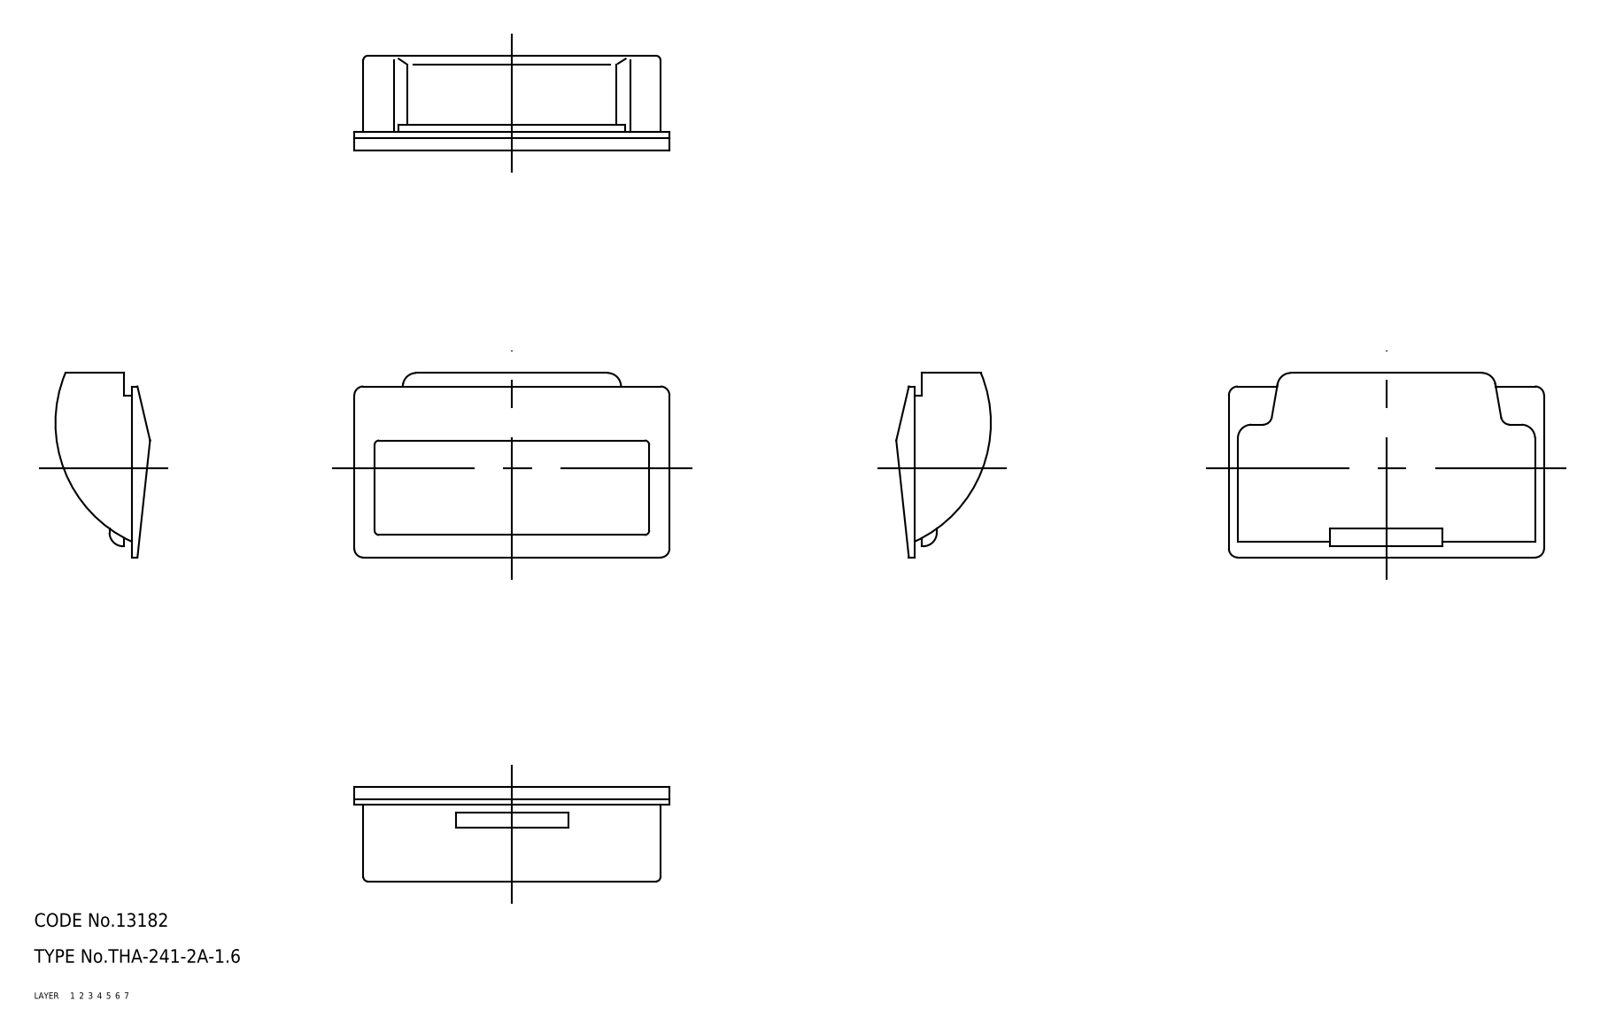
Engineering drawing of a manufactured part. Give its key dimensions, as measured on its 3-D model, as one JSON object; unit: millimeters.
{"part_name": "67113762", "step_written_by": "CADfix (AUTOMOTIVE_DESIGN)", "units": "millimeters", "bodies": {"solids": 1, "faces": 82, "planar": 0, "cylindrical": 0, "other": 82}, "overall_size": [70, 41, 21], "volume_mm3": 14183, "surface_area_mm2": 11743}
